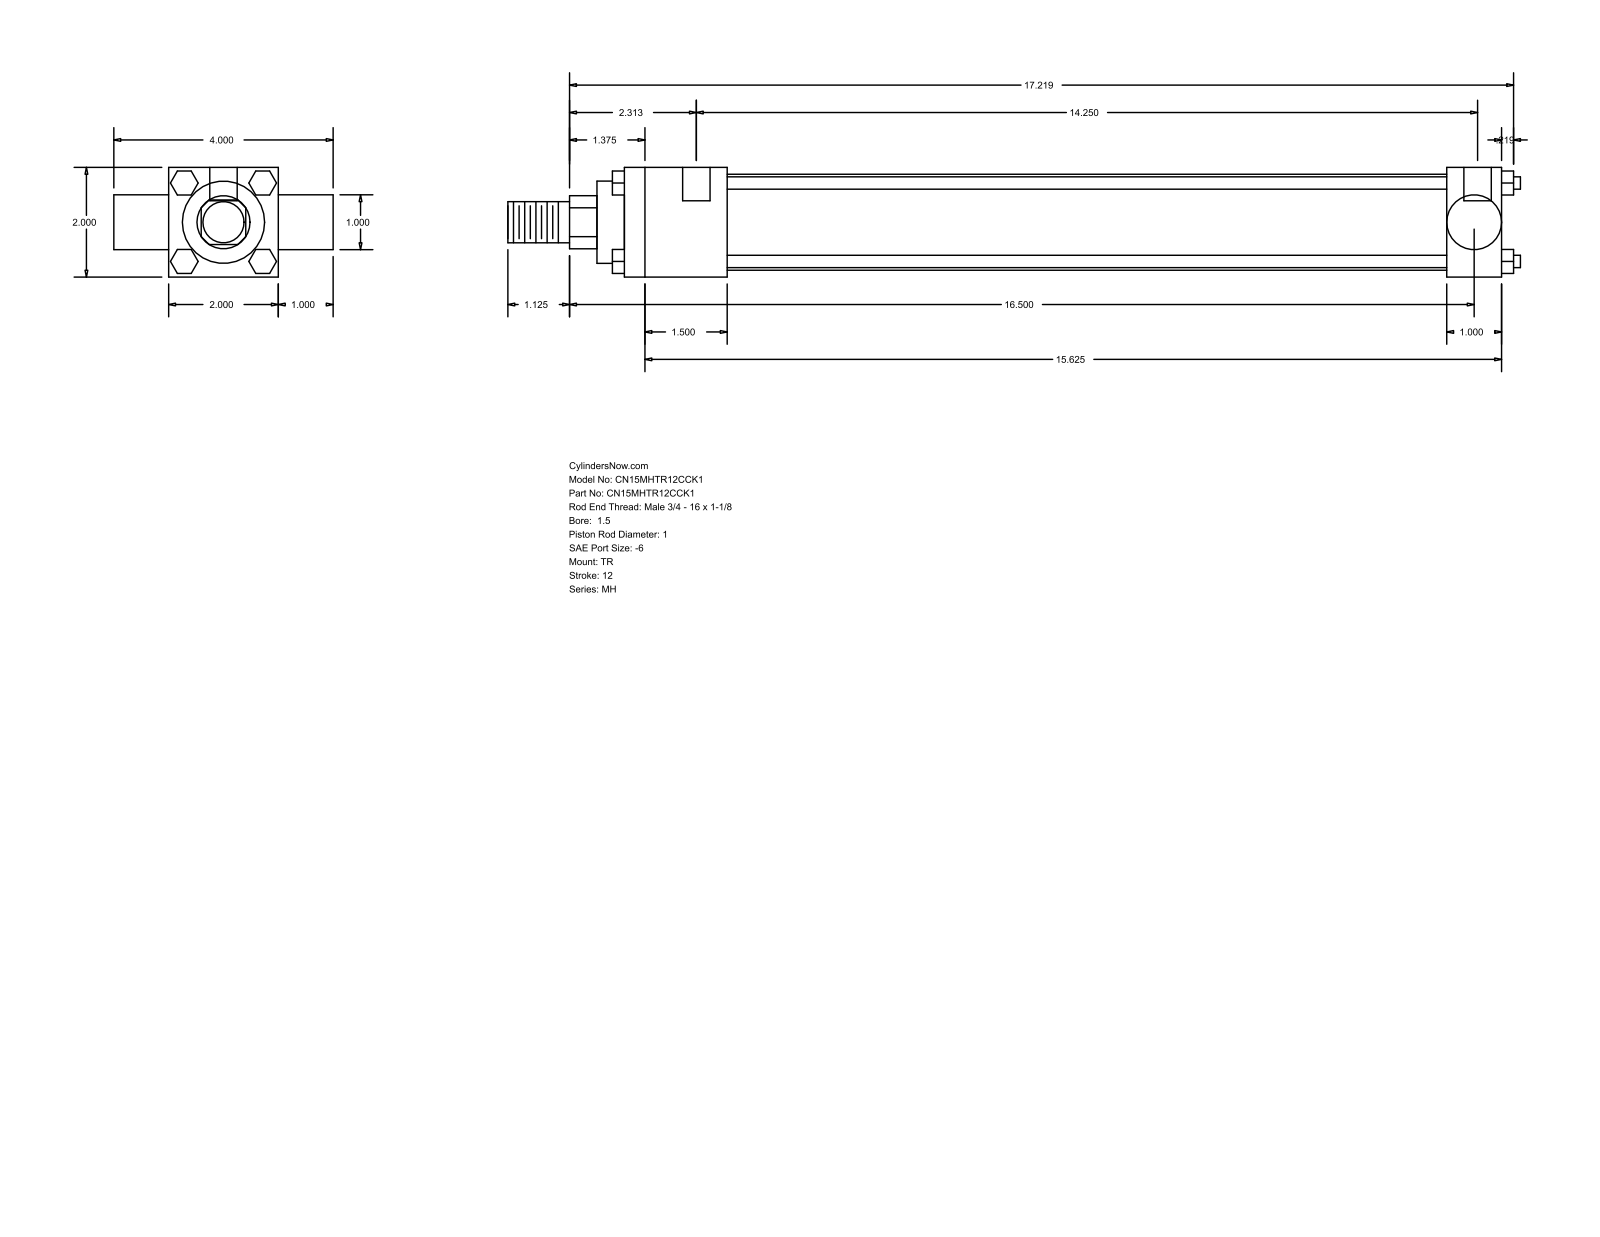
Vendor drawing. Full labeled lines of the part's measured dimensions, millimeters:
Part name (STEP PRODUCT): MH_TR__0150_1
STEP written by: GSSL Pune (CONFIG_CONTROL_DESIGN)
Units: millimetres
Bodies: 0 solids, 120 faces (92 planar, 28 cylindrical, 0 other)
Overall size (bounding box): 469.11 × 101.6 × 50.8
Round holes (diameter × count): ⌀5.56 ×3, ⌀12.7 ×2
Round bosses / shafts (diameter × count): ⌀5.71 ×4, ⌀44.45 ×1, ⌀38.1 ×1, ⌀25.4 ×1, ⌀25.35 ×1, ⌀19.05 ×1
Partial cylindrical surfaces — rounded edges, fillets, slot ends (radius × count): R12.29 ×1
Main face-to-face distances: 50.8, 25.4, 406.4, 76.2, 47.63, 358.77, 381, 333.37, 101.6, 12.7
Hole centre spacings: 3.18, 361.95, 365.13
